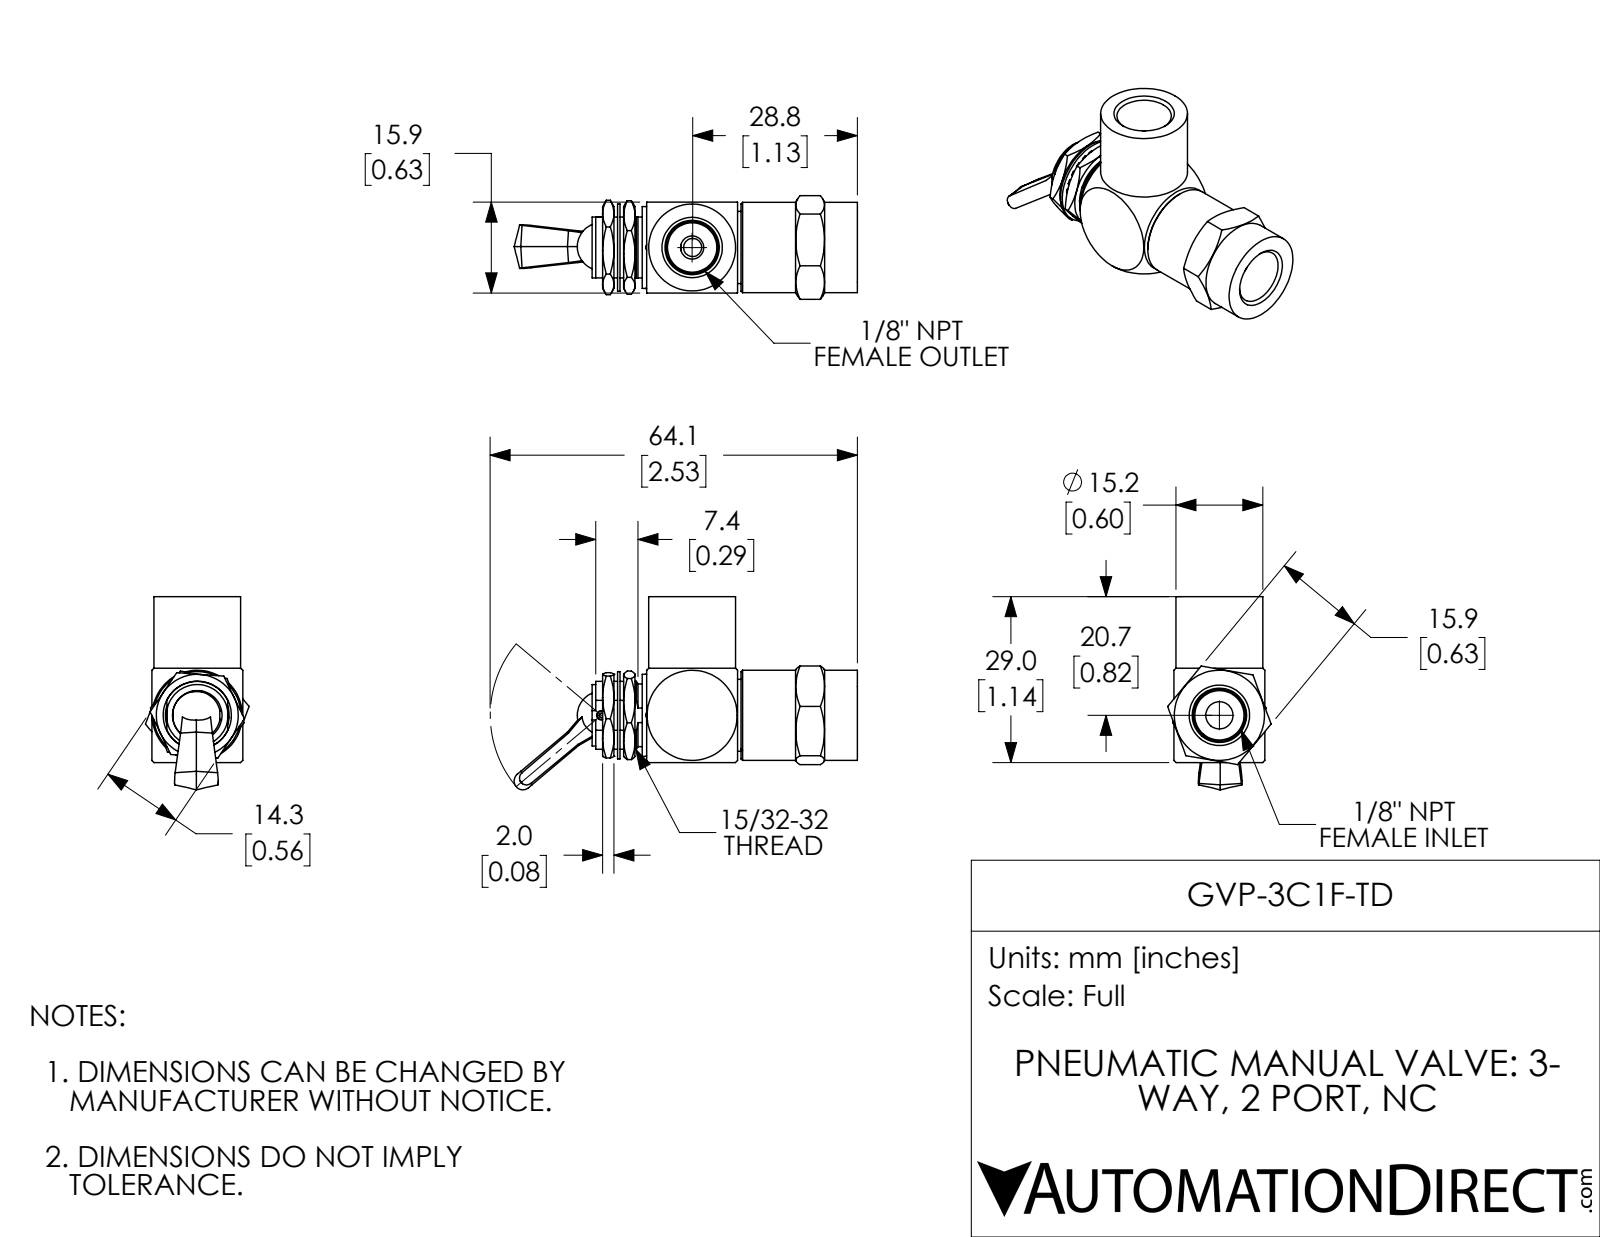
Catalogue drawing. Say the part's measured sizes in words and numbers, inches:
The part is named "GVP-3C1F-TD". Its 3-D file was written by "SolidWorks 2018 (AUTOMOTIVE_DESIGN)". It is 8 solids with 324 faces: 119 planar, 134 cylindrical and 71 other. Overall it measures 2.361 by 1.327 by 0.711 inches. Its volume is 0.52 cubic inches and its surface area 13.43 square inches. Round holes: 3 of diameter 0.063, 2 of diameter 0.125, 2 of diameter 0.339, 1 of diameter 0.03, 1 of diameter 0.07, 1 of diameter 0.159, 1 of diameter 0.187, 1 of diameter 0.249, 1 of diameter 0.34, 1 of diameter 0.377, 1 of diameter 0.438, 1 of diameter 0.468. Round bosses or shafts: 1 of diameter 0.62, 1 of diameter 0.6, 1 of diameter 0.597, 1 of diameter 0.563, 1 of diameter 0.495, 1 of diameter 0.445, 1 of diameter 0.43, 1 of diameter 0.423. Partial cylindrical surfaces (rounded edges, fillets, slot ends): 1 of radius 0.233, 1 of radius 0.239, 1 of radius 0.26. The main face-to-face distances are 0.625, 0.072, 0.52, 0.332, 0.304, 0.128, 0.267, 0.025, 0.042, 0.103. The hole center spacings are 0.291, 0.288, 0.338, 0.629.
